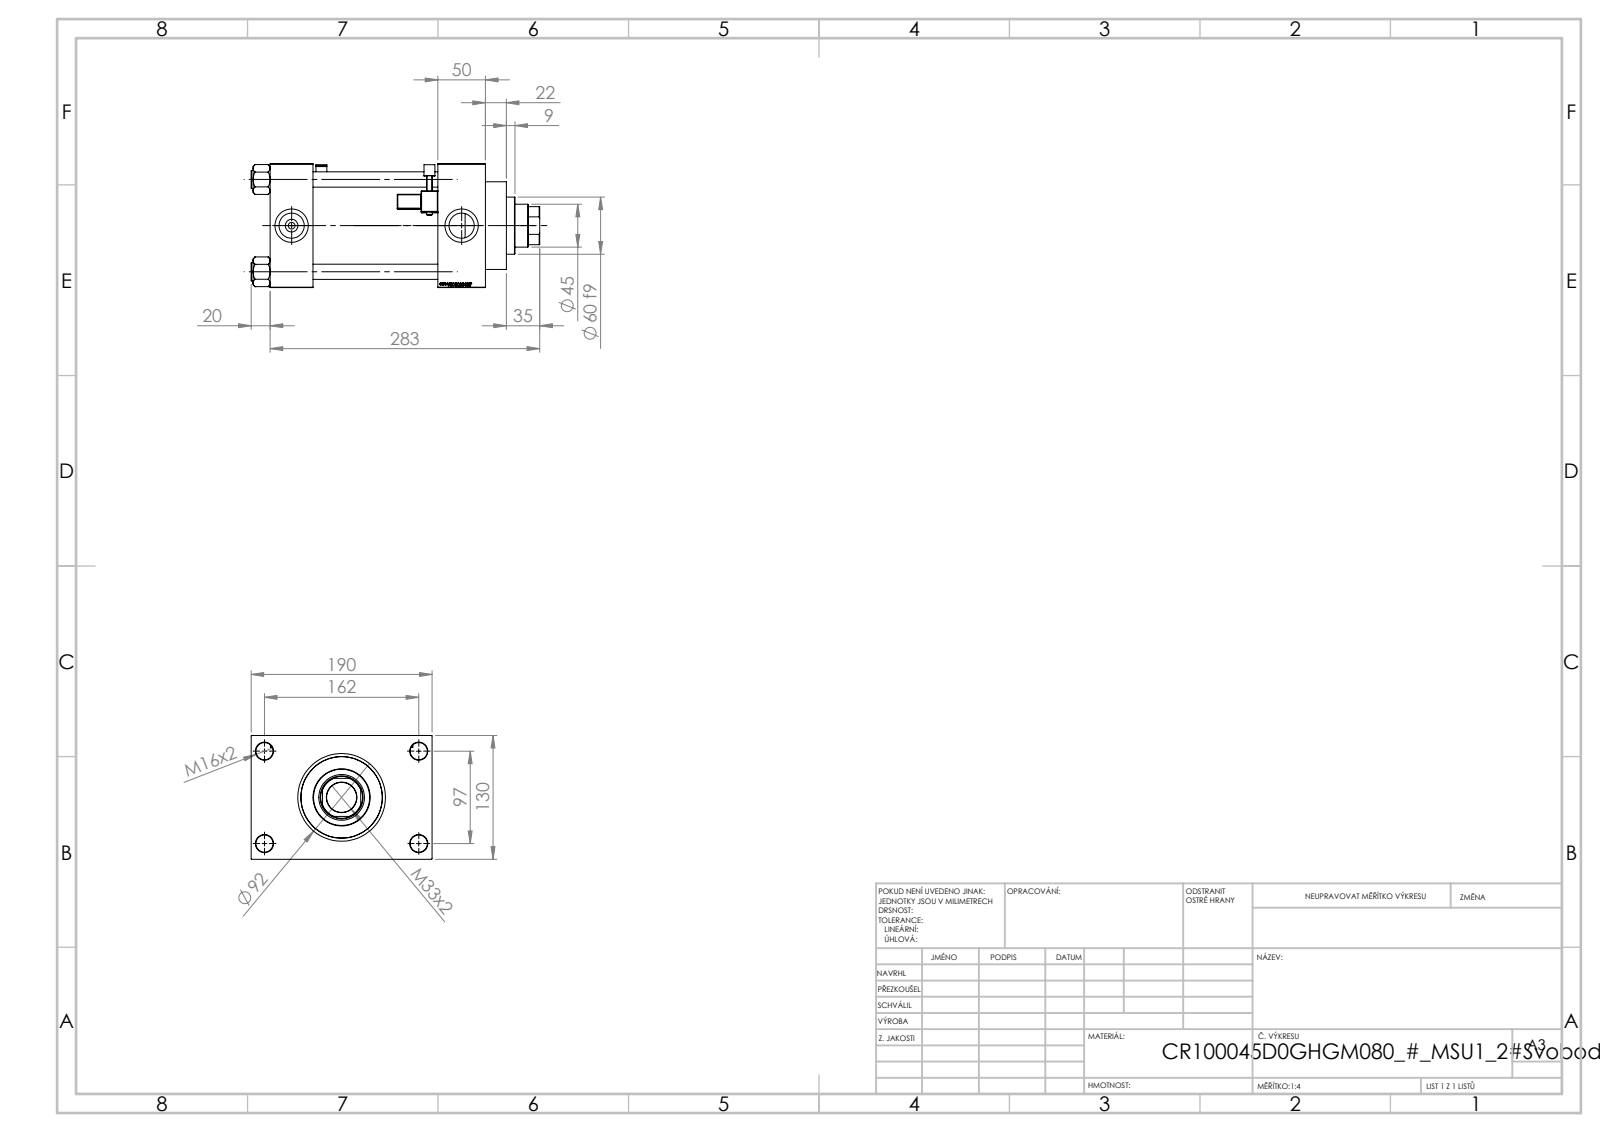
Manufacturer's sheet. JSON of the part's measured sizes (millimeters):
{"part_name": "NUT_M5_D; V215CR_VCP_D; V215CR_D_TYCINKA; V215CR_D_Body (+2 more)", "step_written_by": "SolidWorks 2019 (CONFIG_CONTROL_DESIGN)", "units": "millimeters", "bodies": {"solids": 13, "faces": 1305, "planar": 603, "cylindrical": 148, "other": 554}, "overall_size": [303, 190, 130], "volume_mm3": 2834000, "surface_area_mm2": 426705, "round_holes": [[16, 4], [18, 4], [7, 2], [26.44, 2], [35, 2], [31.5, 1], [45, 1], [48, 1], [76, 1], [85.5, 1], [100, 1]], "round_bosses_or_shafts": [[19, 4], [6, 2], [106, 1], [92, 1], [60, 1]], "partial_cylinders_radius": [[0.5, 48], [1, 2], [2.5, 2], [4, 2], [22, 1]], "face_to_face_distances": [130, 45, 131, 176, 226, 181, 50, 30, 160, 80], "hole_center_spacings": [32.55, 68.52, 94.41, 96.9, 102.27, 129.45, 161.73, 97]}
